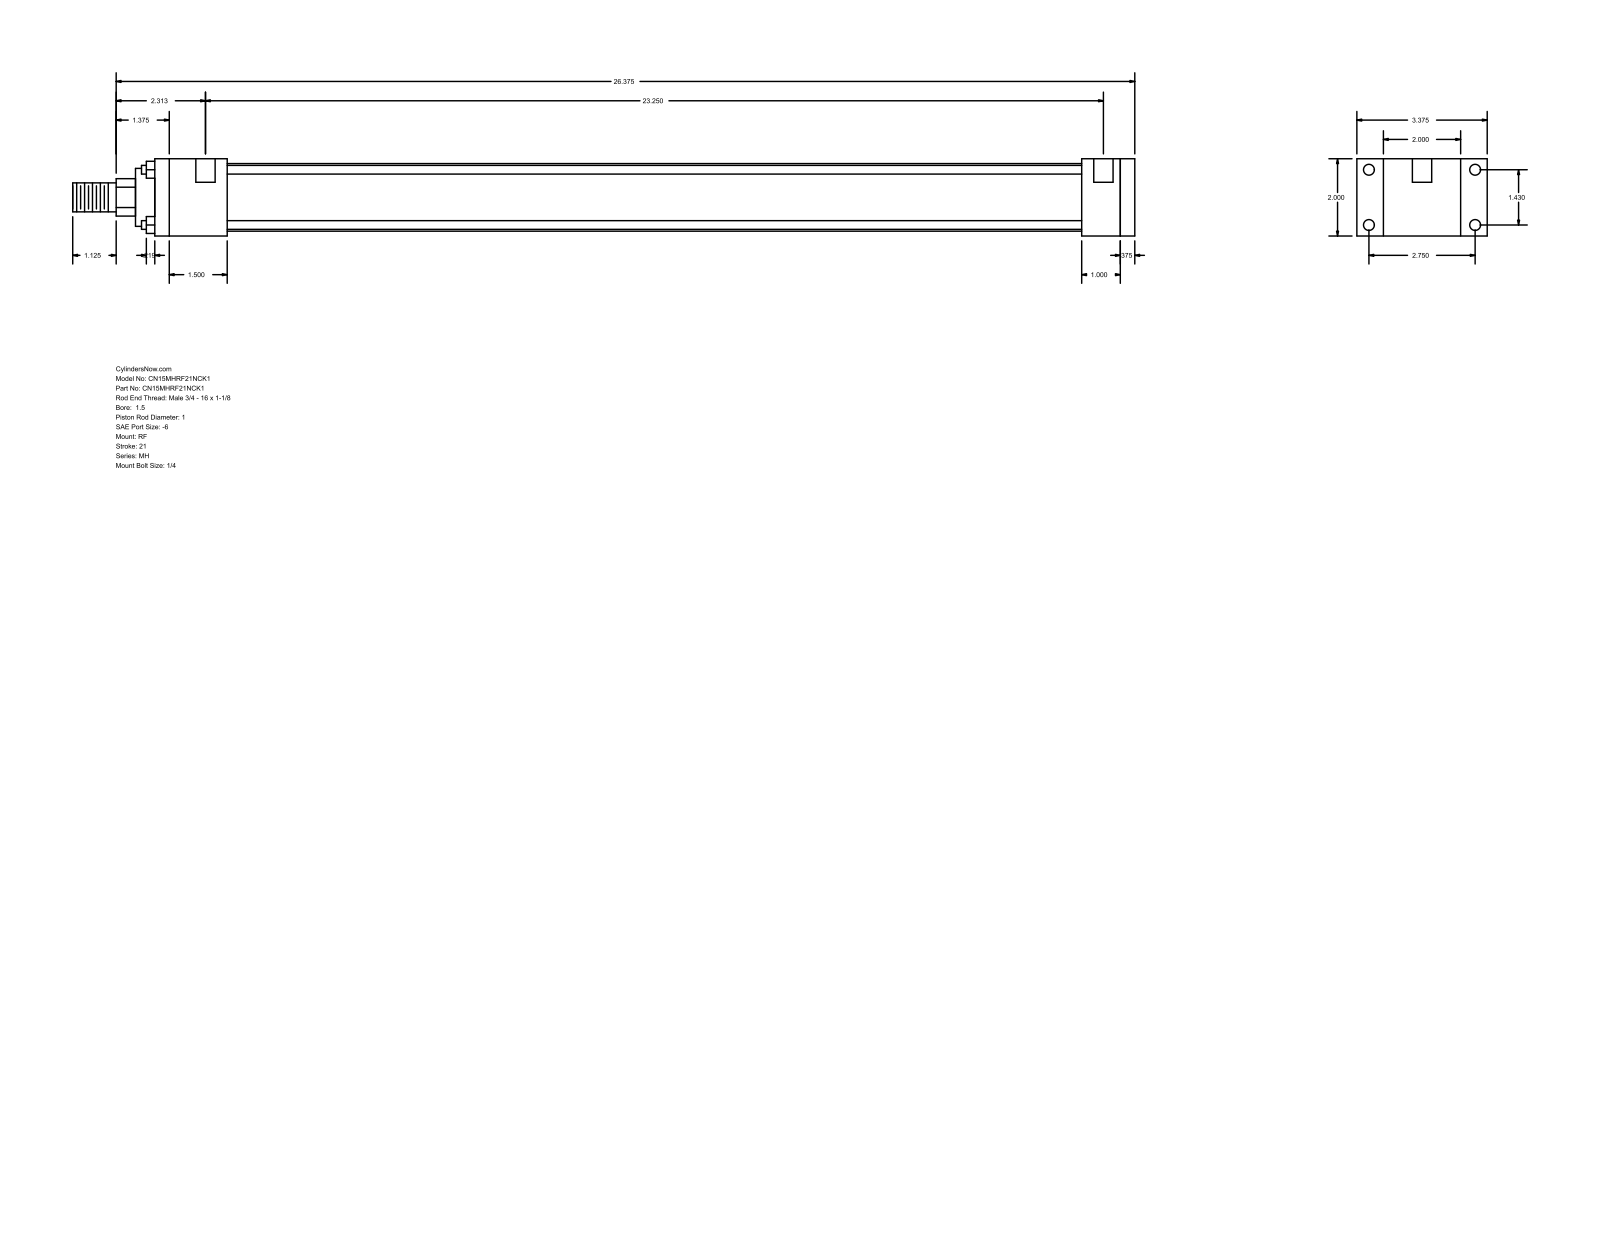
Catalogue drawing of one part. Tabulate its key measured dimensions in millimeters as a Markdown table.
| quantity | value |
| --- | --- |
| part name | MH_RF__0150_1 |
| STEP written by | GSSL Pune (CONFIG_CONTROL_DESIGN) |
| units | millimeters |
| bodies | 0 solids, 92 faces (64 planar, 28 cylindrical, 0 other) |
| overall size | 698.5 × 85.72 × 50.8 |
| round holes (diameter × count) | 5.56 × 4, 7.14 × 4, 12.7 × 2 |
| round bosses / shafts (diameter × count) | 5.71 × 4, 44.45 × 1, 38.1 × 1, 25.4 × 1, 19.05 × 1 |
| partial cylindrical surfaces (radius × count) | 12.29 × 1 |
| main face-to-face distances | 50.8, 9.52, 635, 25.4, 644.52, 17.46, 68.26, 609.6, 34.92, 47.63 |
| hole center spacings | 36.32, 69.84, 78.72, 593.73, 3.18, 590.55 |
